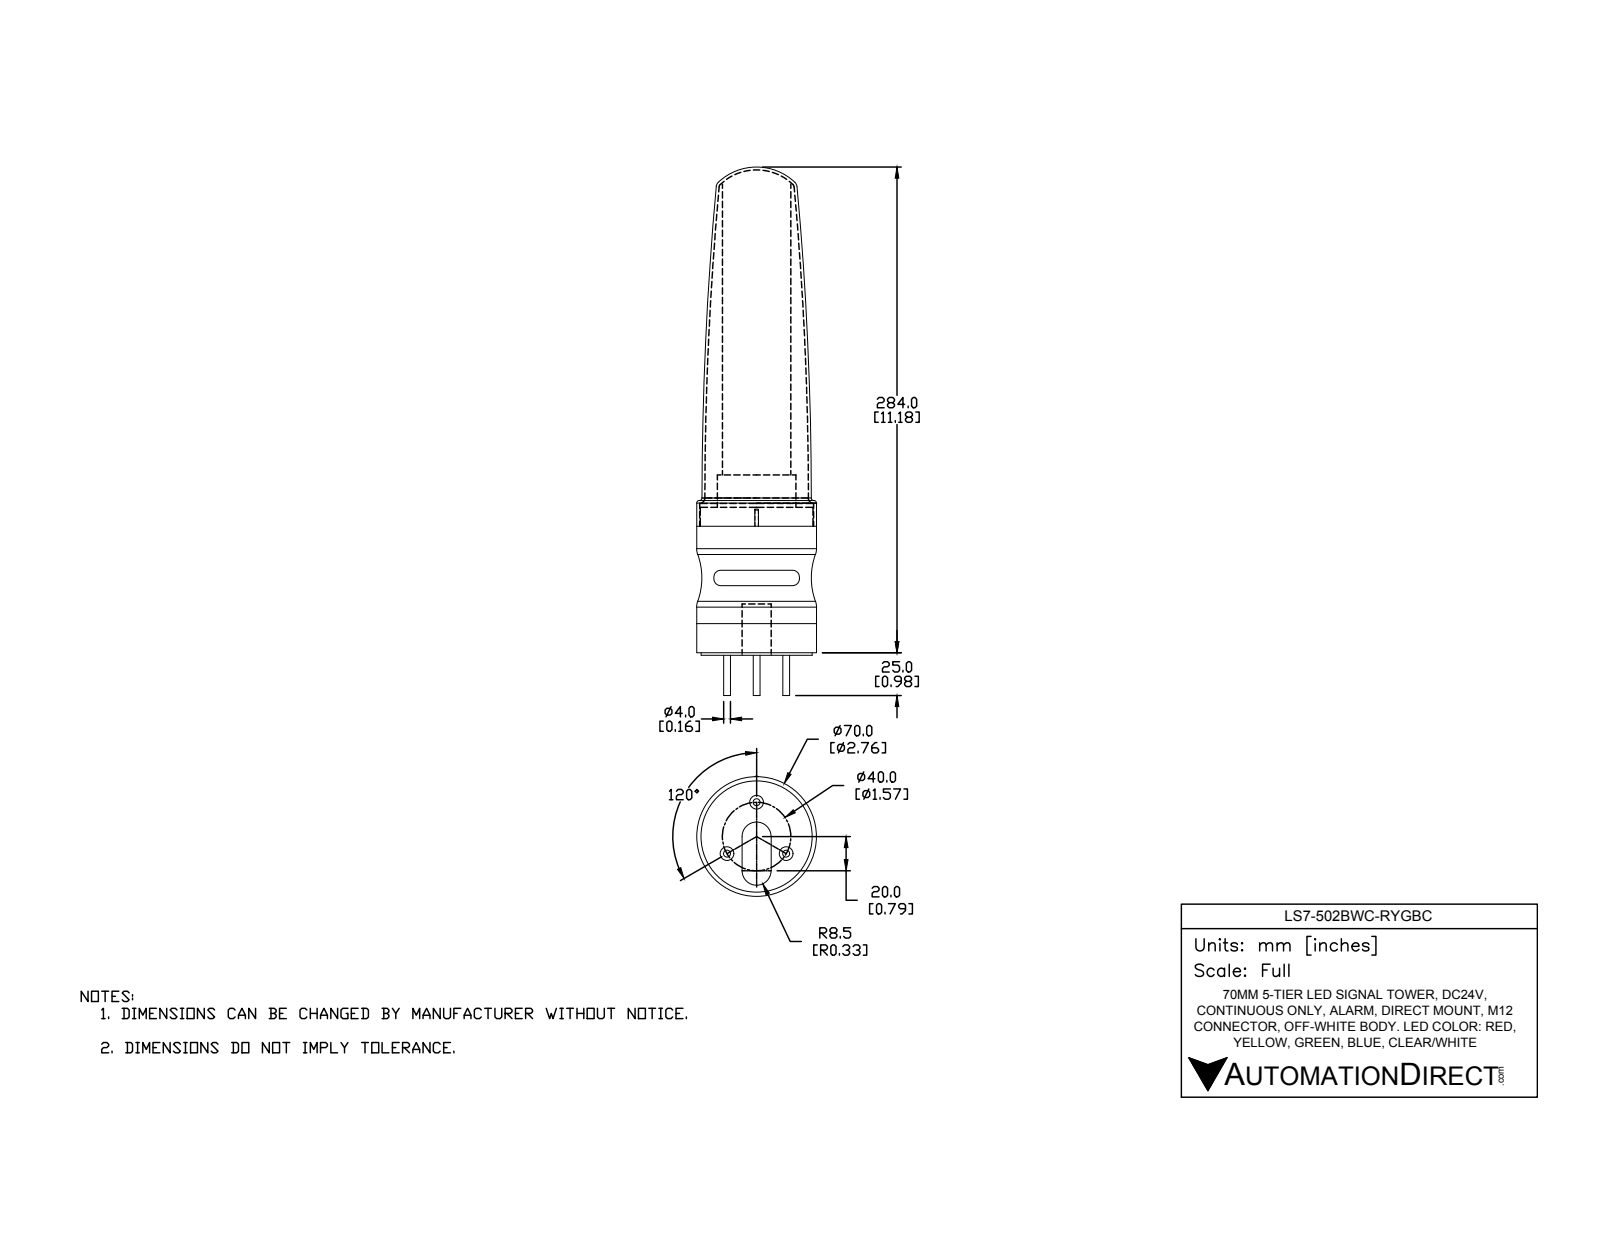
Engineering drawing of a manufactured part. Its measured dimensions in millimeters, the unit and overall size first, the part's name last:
Units: millimetres
Overall size (bounding box): 309 × 70.3 × 70
Round holes (diameter × count): ⌀8 ×3, ⌀66.6 ×1
Round bosses / shafts (diameter × count): ⌀4 ×3, ⌀70 ×1, ⌀66 ×1, ⌀65 ×1, ⌀46 ×1, ⌀40 ×1
Partial cylindrical surfaces — rounded edges, fillets, slot ends (radius × count): R4 ×4, R8.5 ×2, R1 ×1, R2 ×1
Main face-to-face distances: 17, 104, 87, 1.5, 18.5, 105.5, 86.5, 85, 68, 19
Hole centre spacings: 20, 34.64
Volume: 595 853 mm³ · Surface area: 148 747 mm²
Bodies: 8 solids, 101 faces (32 planar, 45 cylindrical, 24 other)
Part name (STEP PRODUCT): LS7-502BWC-RYGBC
STEP written by: SolidWorks 2016 (AUTOMOTIVE_DESIGN)
